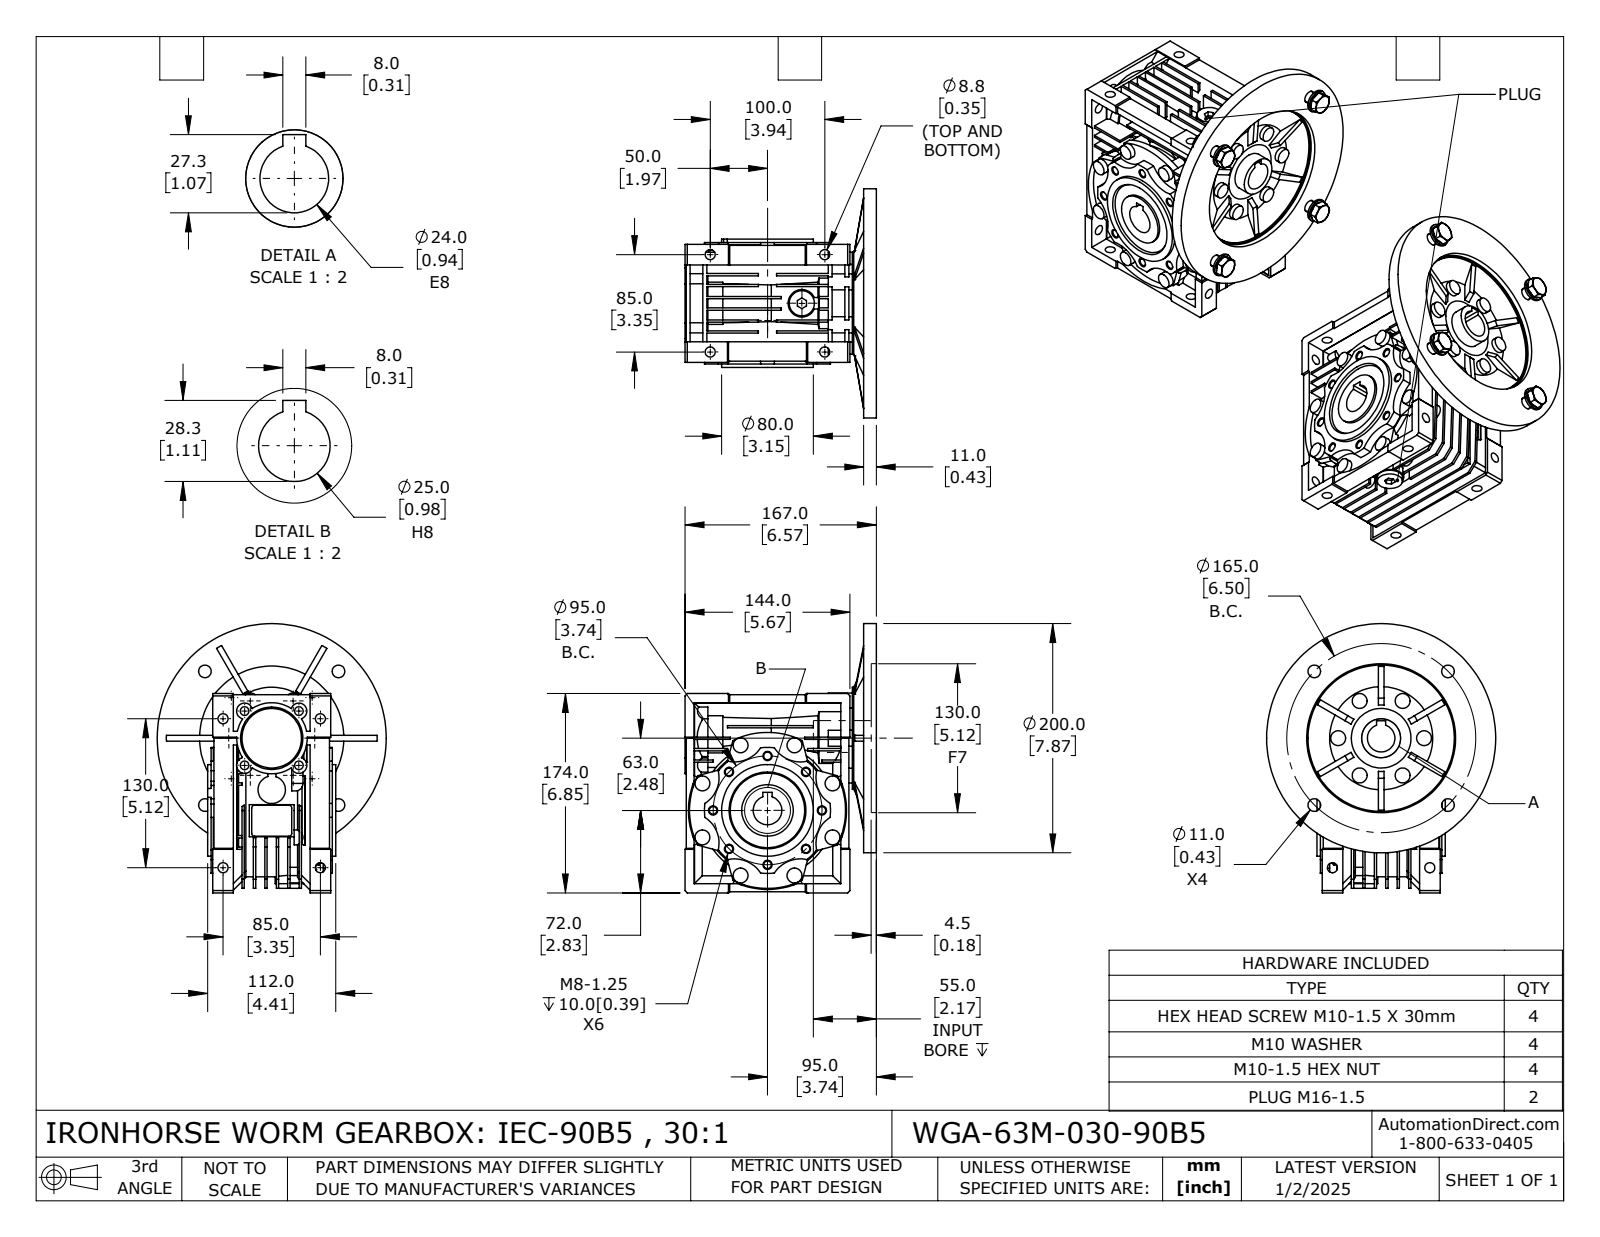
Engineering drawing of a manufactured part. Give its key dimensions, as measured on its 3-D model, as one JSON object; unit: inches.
{"part_name": "WGA-63M-030-90B5", "step_written_by": "SolidWorks 2024 (CONFIG_CONTROL_DESIGN)", "units": "inches", "bodies": {"solids": 20, "faces": 1529, "planar": 897, "cylindrical": 394, "other": 238}, "overall_size": [9.252, 7.874, 7.222], "volume_in3": 123.3, "surface_area_in2": 624.5, "round_holes": [[0.262, 8], [0.346, 8], [0.298, 4], [0.335, 4], [0.394, 4], [0.413, 4], [0.433, 4], [0.571, 2], [0.984, 2], [0.945, 1], [1.339, 1], [1.457, 1]], "round_bosses_or_shafts": [[0.512, 14], [0.787, 4], [0.63, 4], [0.945, 3], [0.866, 2], [0.622, 2], [0.539, 2], [7.874, 1]], "partial_cylinders_radius": [[0.276, 10], [1.063, 8], [0.098, 4], [0.329, 1], [1.161, 1], [1.201, 1], [1.654, 1], [1.811, 1]], "face_to_face_distances": [0.394, 0.315, 0.787, 0.079, 0.433, 1.181, 0.472, 0.276, 1.575, 0.709], "hole_center_spacings": [1.431, 1.87, 2.645, 3.456, 3.506, 1.319, 1.865, 1.929]}
